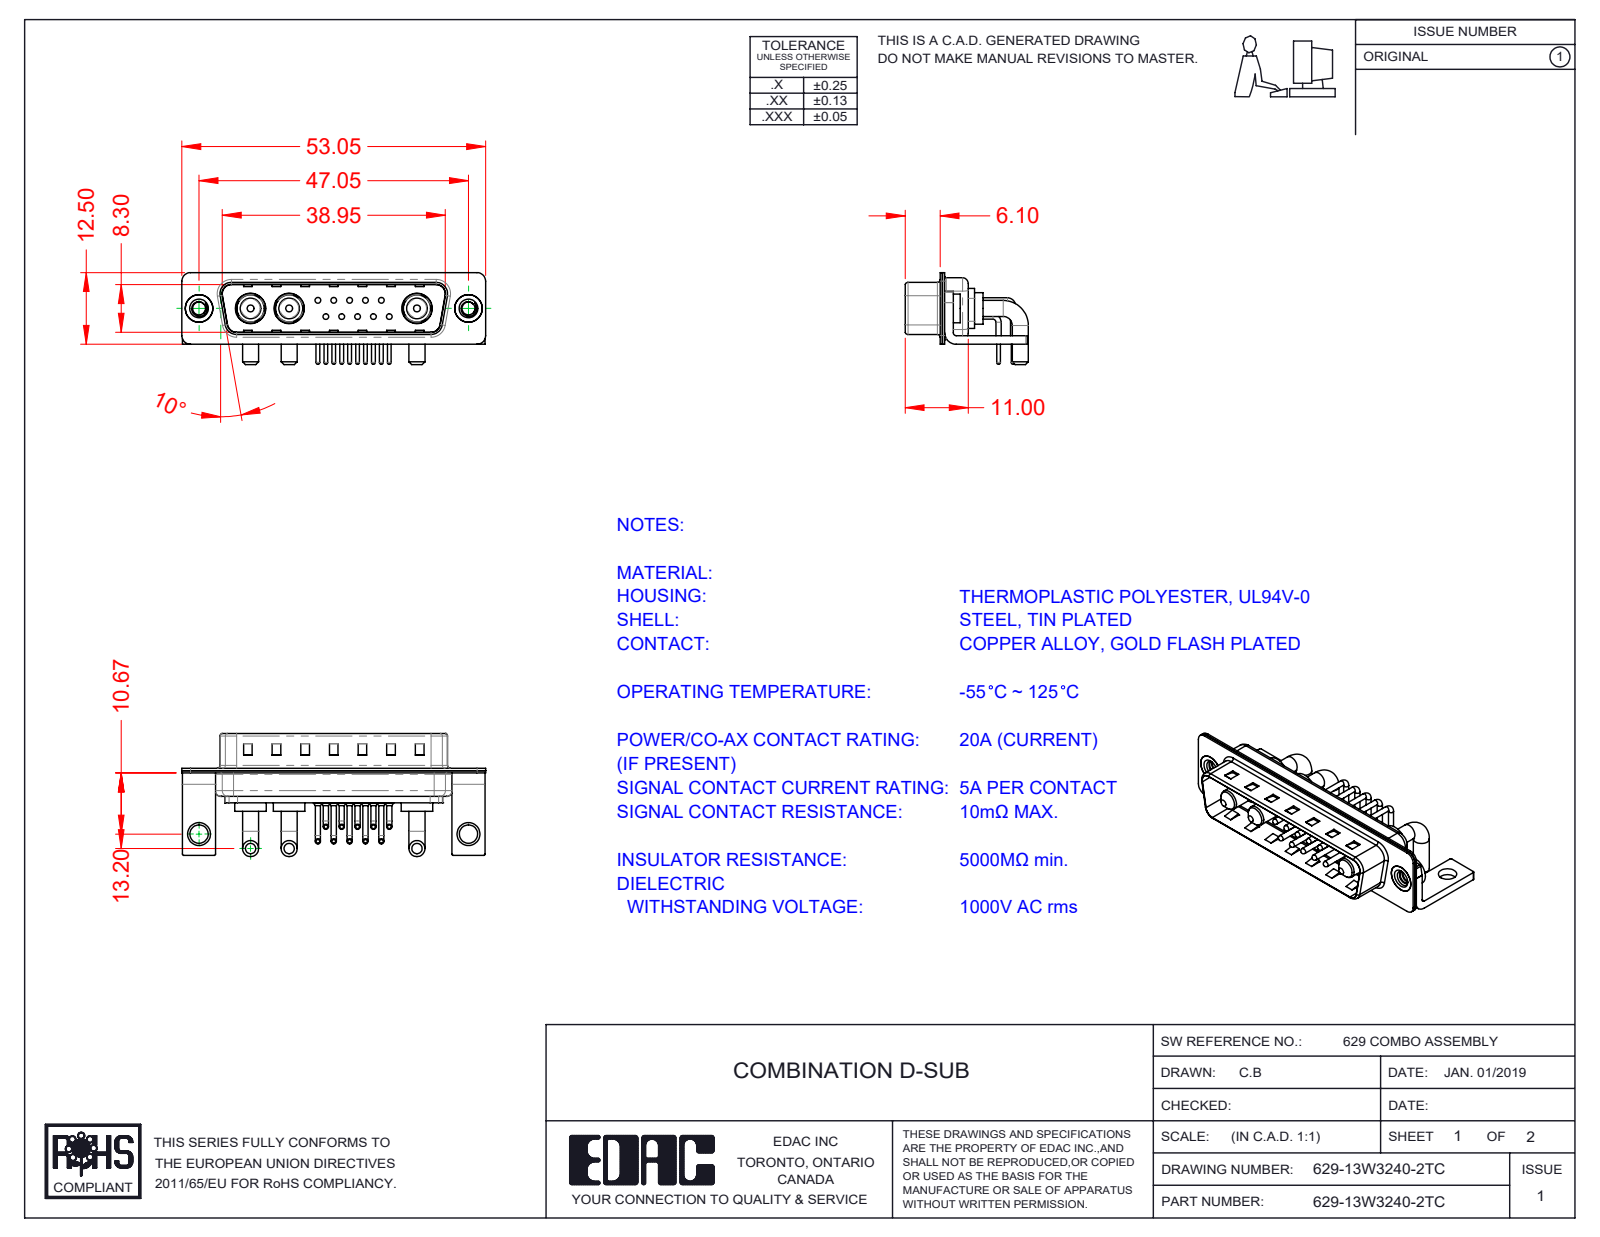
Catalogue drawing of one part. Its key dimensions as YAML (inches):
part_name: "Power Pin_20A RA; 629Combo Shell Front_25 Contacts; 629Combo Housing_13W3; 629Combo Stabilizer Bracket (+5 more)"
step_written_by: "SolidWorks 2020 (CONFIG_CONTROL_DESIGN)"
units: inches
bodies: {solids: 23, faces: 1653, planar: 861, cylindrical: 584, other: 208}
overall_size: [2.089, 0.846, 0.632]
volume: 0.215
surface_area: 12.42
round_holes:
  - {diameter: 0.03, count: 10}
  - {diameter: 0.063, count: 10}
  - {diameter: 0.079, count: 10}
  - {diameter: 0.191, count: 3}
  - {diameter: 0.209, count: 3}
  - {diameter: 0.089, count: 2}
  - {diameter: 0.126, count: 2}
  - {diameter: 0.157, count: 2}
  - {diameter: 0.189, count: 2}
round_bosses_or_shafts:
  - {diameter: 0.035, count: 20}
  - {diameter: 0.059, count: 10}
  - {diameter: 0.039, count: 10}
  - {diameter: 0.026, count: 10}
  - {diameter: 0.11, count: 6}
  - {diameter: 0.217, count: 3}
  - {diameter: 0.205, count: 3}
  - {diameter: 0.187, count: 3}
partial_cylinders:
  - {radius: 0.01, count: 16}
  - {radius: 0.059, count: 16}
  - {radius: 0.079, count: 13}
  - {radius: 0.04, count: 10}
  - {radius: 0.02, count: 9}
  - {radius: 0.063, count: 8}
  - {radius: 0.024, count: 4}
  - {radius: 0.026, count: 4}
face_to_face_distances: [0.016, 0.031, 0.374, 0.059, 0.358, 0.343, 0.39, 0.024, 0.205, 0.047]
hole_center_spacings: [0.124, 0.109, 0.198, 0.218, 0.295, 0.198, 0.327, 0.398]
